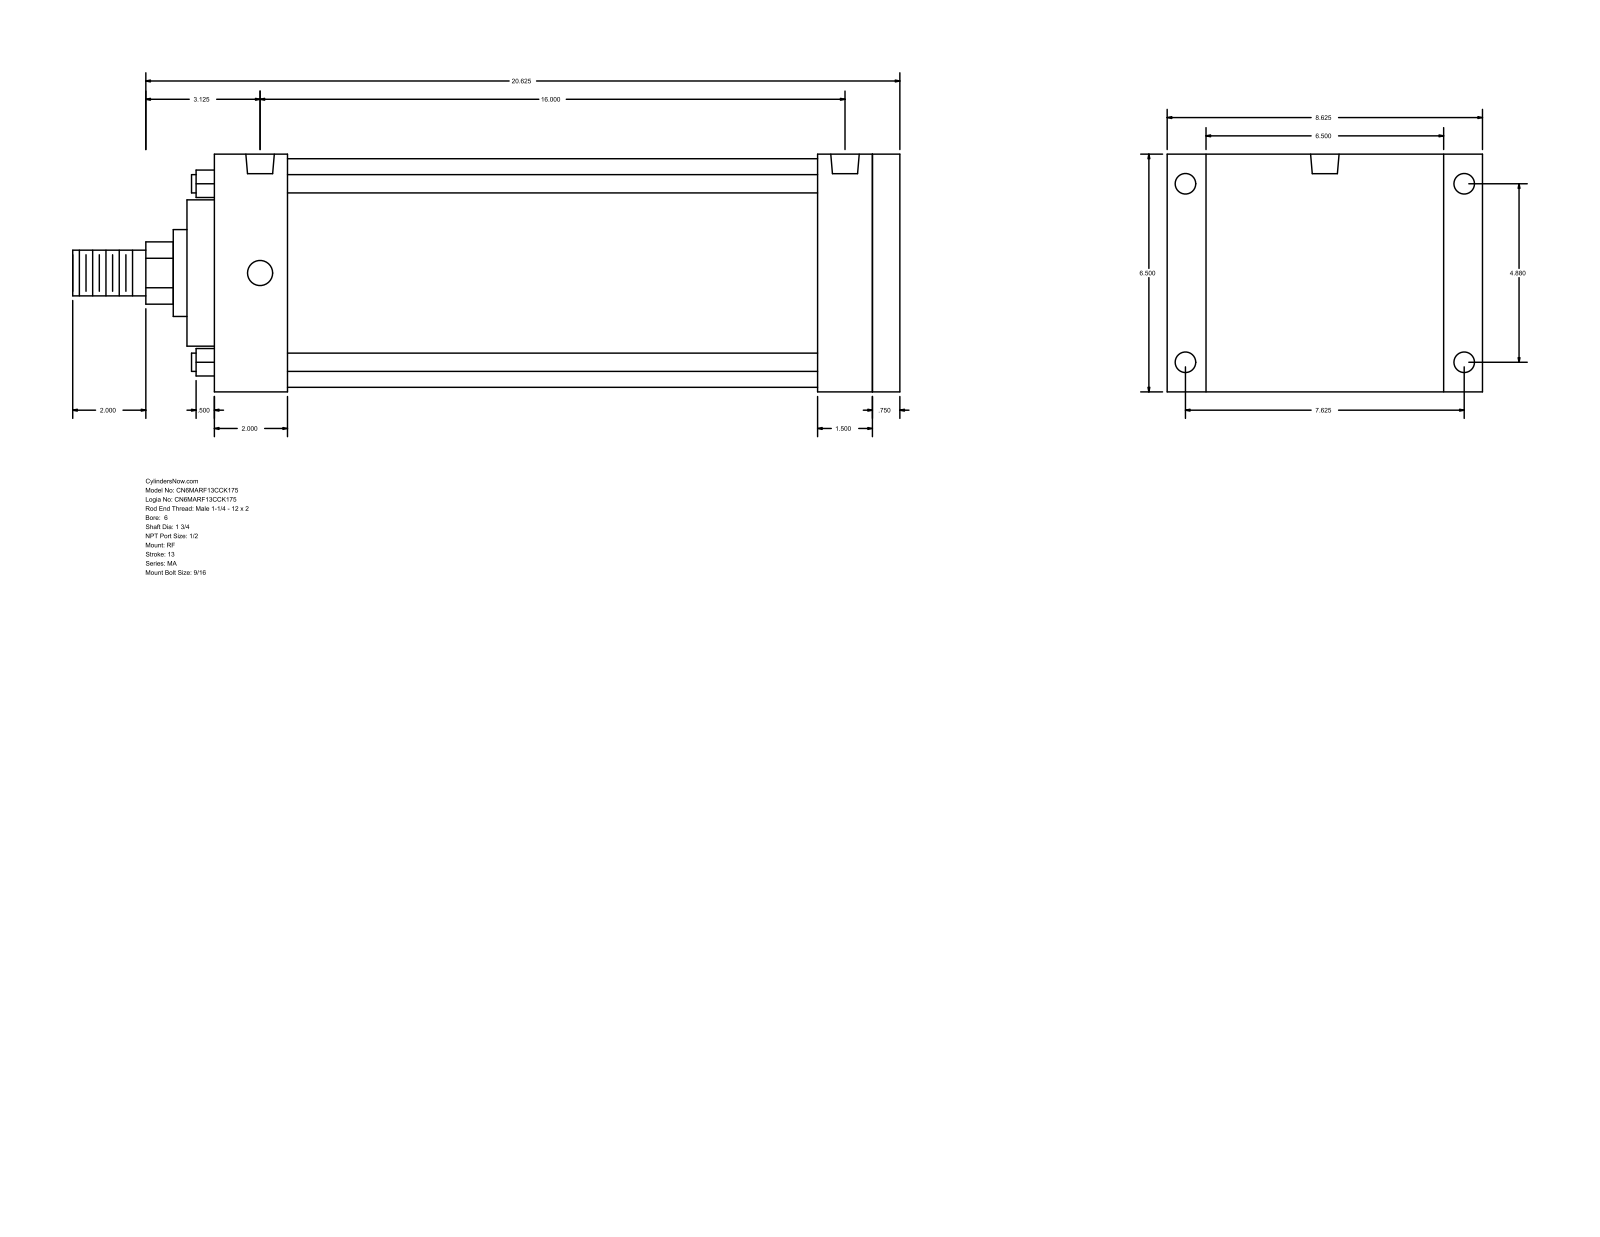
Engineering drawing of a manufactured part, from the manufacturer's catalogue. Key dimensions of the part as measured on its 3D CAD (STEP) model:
Part name (STEP PRODUCT): MA_RF__0600_1.75
STEP written by: GSSL Pune (CONFIG_CONTROL_DESIGN)
Units: millimetres
Bodies: 0 solids, 94 faces (65 planar, 29 cylindrical, 0 other)
Overall size (bounding box): 574.67 × 219.07 × 165.1
Round holes (diameter × count): ⌀14.29 ×4, ⌀17.46 ×4, ⌀19.77 ×2
Round bosses / shafts (diameter × count): ⌀12.7 ×4, ⌀158.75 ×1, ⌀101.6 ×1, ⌀60.33 ×1, ⌀44.45 ×1, ⌀31.75 ×1
Partial cylindrical surfaces — rounded edges, fillets, slot ends (radius × count): R21.63 ×1
Main face-to-face distances: 165.1, 476.26, 457.2, 19.06, 50.8, 19.05, 406.4, 425.46, 419.11, 368.31
Hole centre spacings: 123.96, 193.68, 229.95, 406.39
